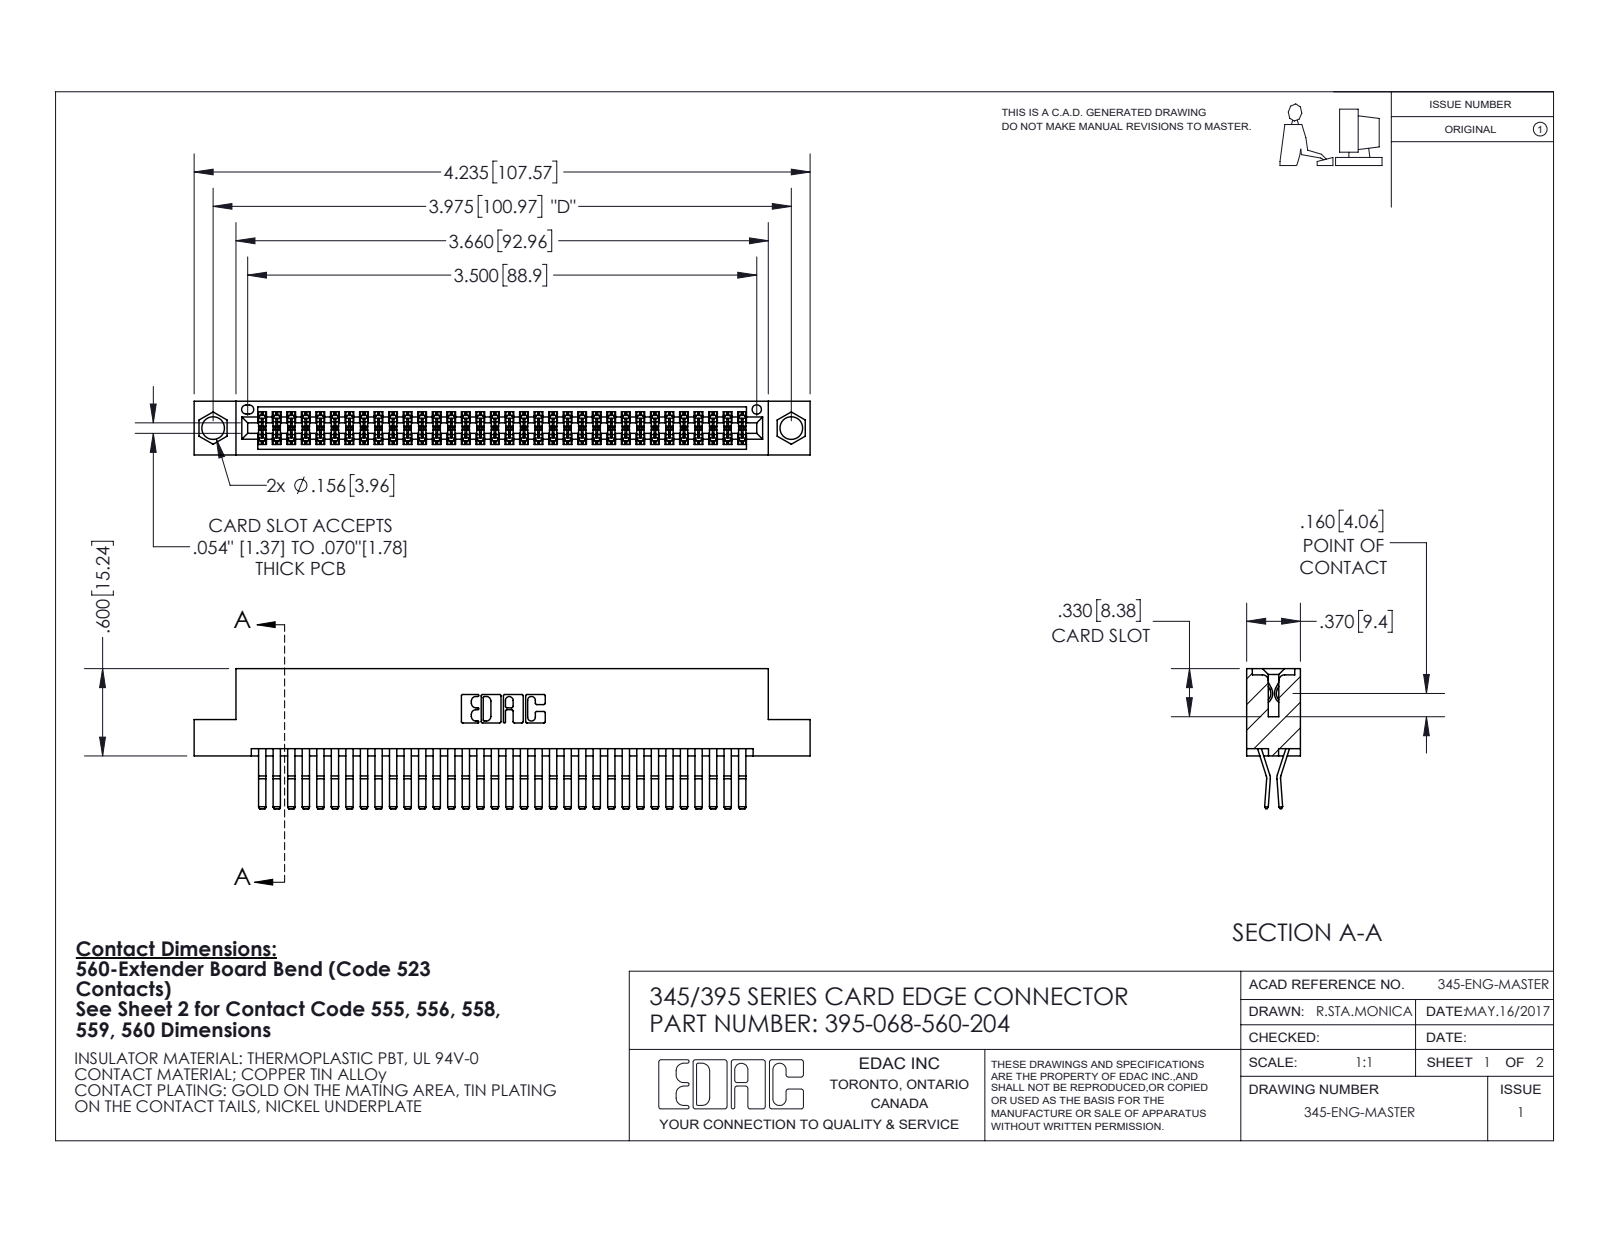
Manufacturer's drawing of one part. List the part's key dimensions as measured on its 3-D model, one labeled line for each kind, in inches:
Part name (STEP PRODUCT): 345-292-001_560 Tail; 345 Part_Flush Mounting Lugs - 0.156 Dia-TI; 395-068-560-204
STEP written by: SolidWorks 2020 (CONFIG_CONTROL_DESIGN)
Units: inches
Bodies: 69 solids, 3676 faces (2338 planar, 1338 cylindrical, 0 other)
Overall size (bounding box): 4.235 × 0.962 × 0.37
Volume: 0.654 in³ · Surface area: 25.86 in²
Round holes (diameter × count): ⌀0.156 ×2, ⌀0.064 ×1
Partial cylindrical surfaces — rounded edges, fillets, slot ends (radius × count): R0.006 ×102, R0.01 ×22, R0.007 ×6, R0.031 ×6, R0.026 ×3, R0.01 ×2, R0.014 ×2, R0.019 ×2
Main face-to-face distances: 0.025, 0.298, 0.072, 0.2, 0.37, 0.098, 0.272, 0.225, 0.175, 0.149
Hole centre spacings: 0.27, 3.74, 3.975
